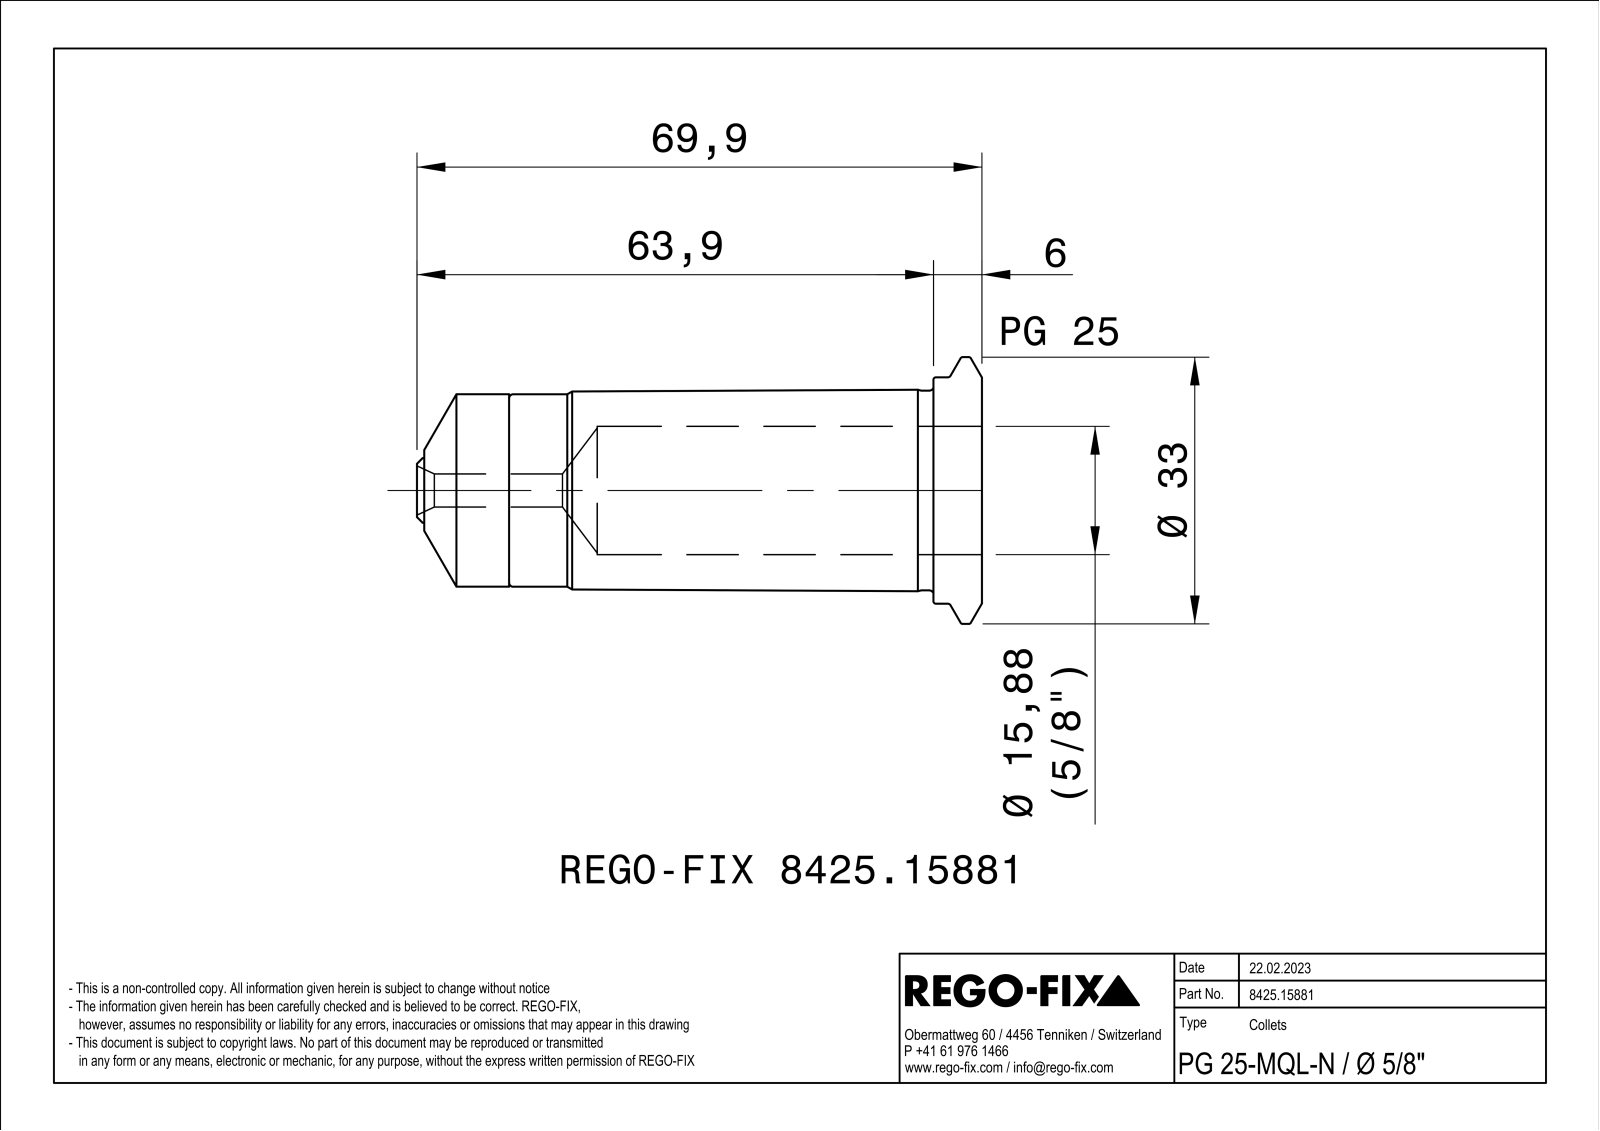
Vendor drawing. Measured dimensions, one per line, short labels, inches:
name: NOCUT
written by: SIEMENS PLM Software Solid Edge ST10 (AUTOMOTIVE_DESIGN)
unit: in
bodies: 1 solid, 78 faces (17 planar, 17 cylindrical, 44 other)
size: 2.752 × 1.299 × 1.299
volume: 0.453 in³; area: 18.79 in²
holes: 1× ⌀0.161, 1× ⌀0.625, 1× ⌀0.824, 1× ⌀0.874
bosses: 1× ⌀1.299, 1× ⌀1.102, 1× ⌀0.972, 1× ⌀0.937, 1× ⌀0.898, 1× ⌀0.315
face distances: 0.039, 2.303, 0.236, 2.067, 1.831, 2.717, 2.48, 0.65, 0.413, 2.051
